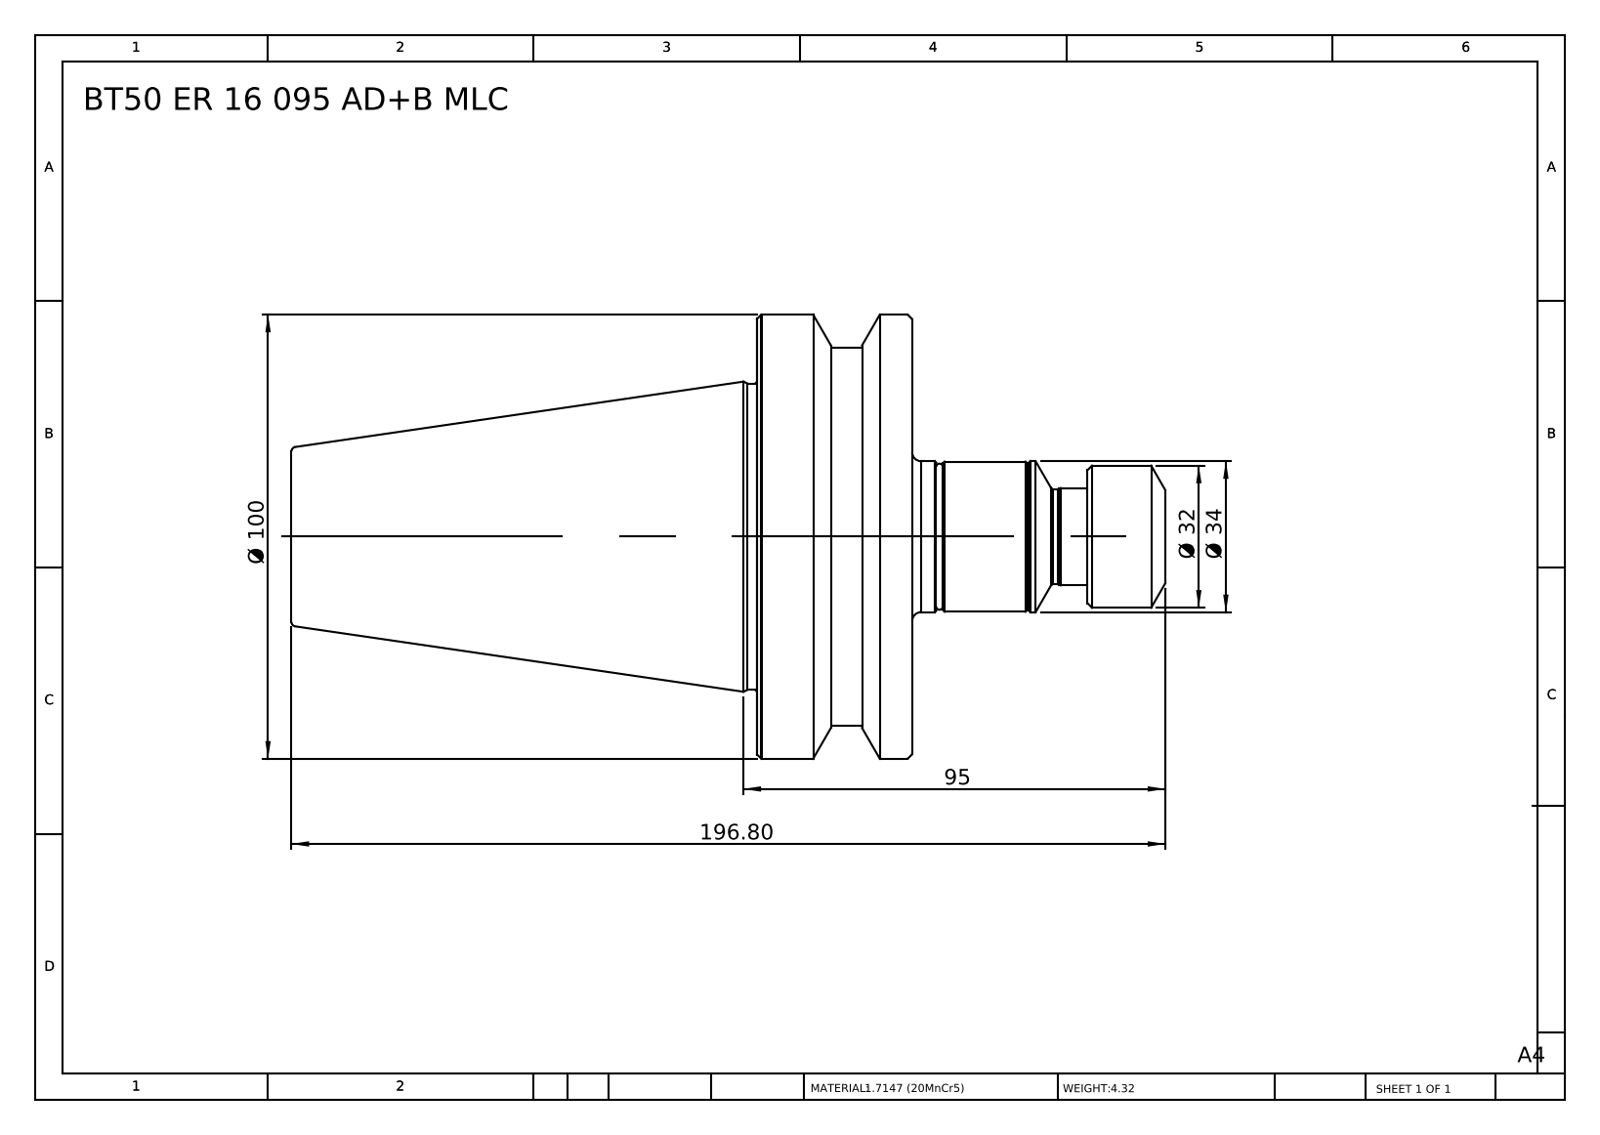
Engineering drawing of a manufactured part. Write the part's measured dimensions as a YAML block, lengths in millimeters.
part_name: "BT50 ER 16 095 AD+B MLC"
step_written_by: "SolidWorks 2014 (CONFIG_CONTROL_DESIGN)"
units: millimeters
bodies: {solids: 1, faces: 81, planar: 11, cylindrical: 22, other: 48}
overall_size: [196.8, 100, 100]
volume: 553434
surface_area: 50814
round_bosses_or_shafts:
  - {diameter: 100, count: 1}
  - {diameter: 85, count: 1}
  - {diameter: 69, count: 1}
  - {diameter: 34, count: 1}
  - {diameter: 33.8, count: 1}
  - {diameter: 32, count: 1}
  - {diameter: 29.9, count: 1}
  - {diameter: 21.9, count: 1}
face_to_face_distances: [35, 139.8, 104.8, 57, 92, 196.8, 17.5, 39.5, 74.5, 179.3]
